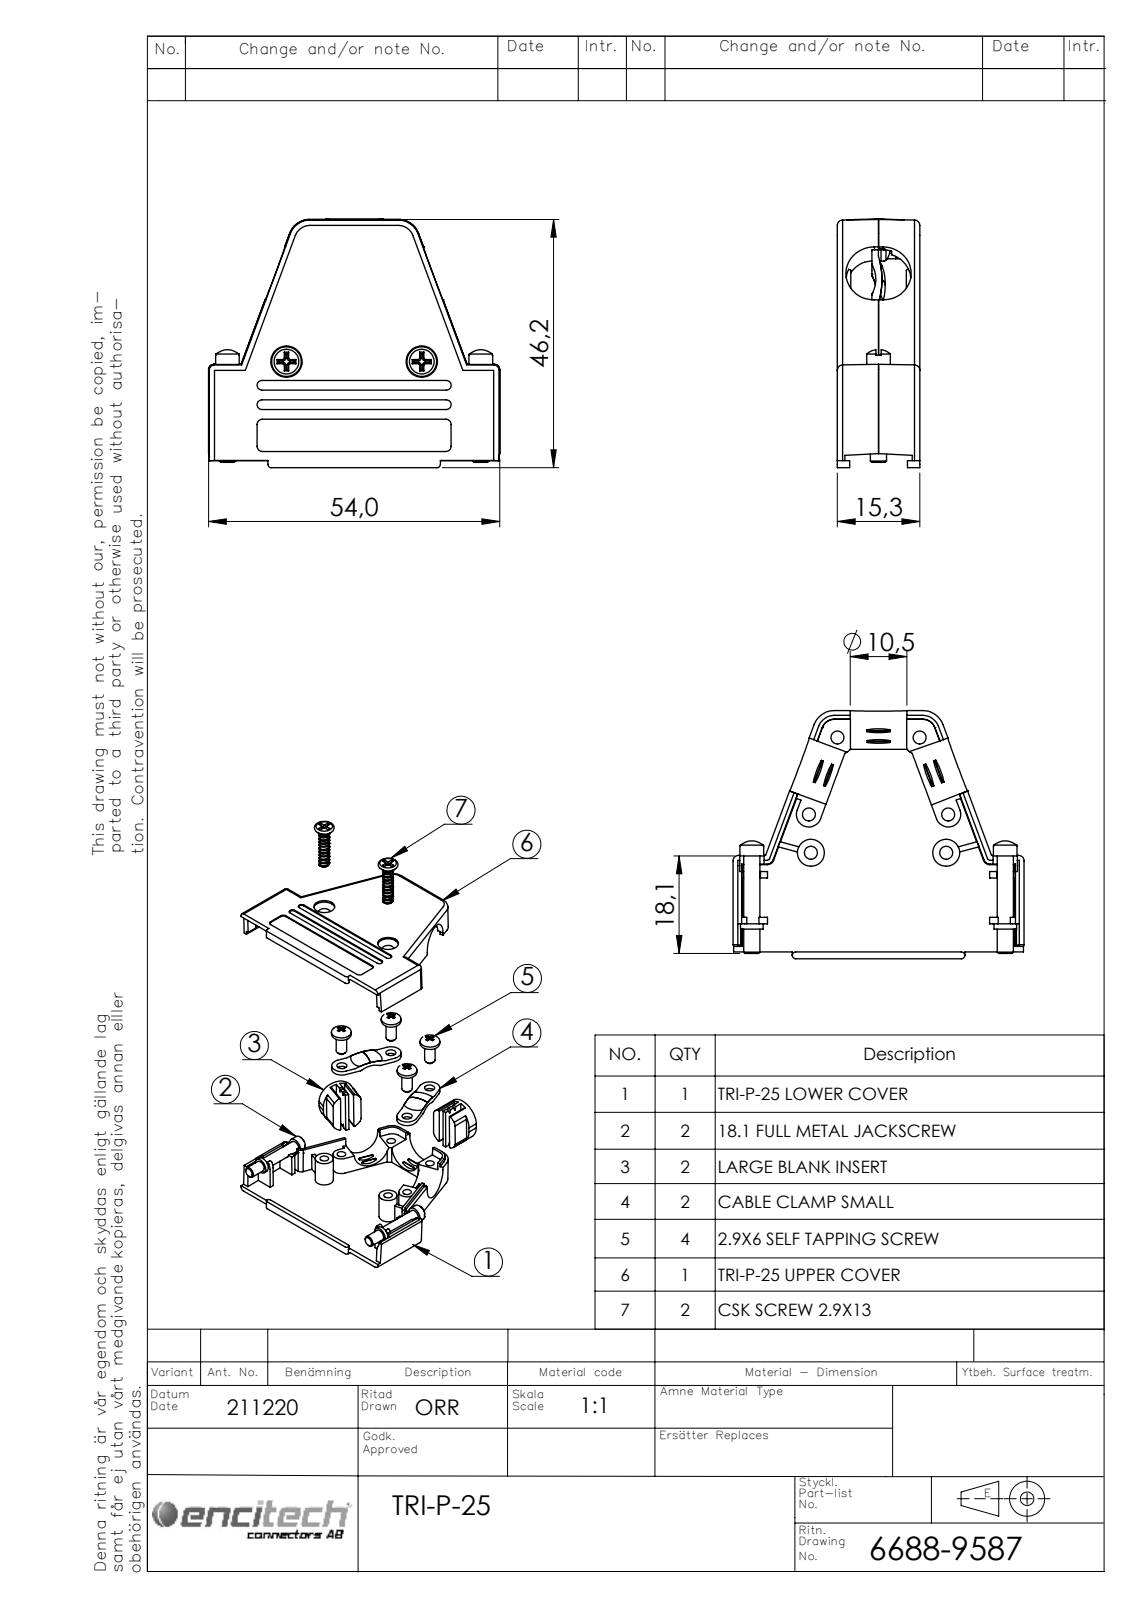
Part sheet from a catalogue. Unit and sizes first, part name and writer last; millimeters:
Units: millimetres
Overall size (bounding box): 54 × 46.19 × 15.3
Round holes (diameter × count): ⌀2.4 ×6, ⌀2.8 ×4, ⌀3.2 ×4, ⌀4.5 ×2, ⌀5.2 ×2, ⌀5.8 ×2
Round bosses / shafts (diameter × count): ⌀5.5 ×4, ⌀3 ×4, ⌀2.9 ×4, ⌀7 ×2, ⌀5 ×2, ⌀4.4 ×2, ⌀4.2 ×2, ⌀2.46 ×2
Partial cylindrical surfaces — rounded edges, fillets, slot ends (radius × count): R1 ×21, R0.5 ×10, R1.25 ×10, R0.25 ×6, R5.25 ×5, R0.9 ×4, R1.5 ×4, R1.79 ×4
Main face-to-face distances: 13.9, 1.4, 15.3, 12.5, 13.6, 1.1, 15, 6.25, 1.6, 7.65
Hole centre spacings: 15.25, 7.11, 15.14, 15.26, 21.96, 26.4, 26.44, 29.41
Volume: 9 866 mm³ · Surface area: 15 095 mm²
Bodies: 17 solids, 833 faces (454 planar, 254 cylindrical, 125 other)
Part name (STEP PRODUCT): 6805-0104-13; 6826-0133-01; 6855-0109-11; 6805-0104-03 (+4 more)
STEP written by: SolidWorks 2021 (AUTOMOTIVE_DESIGN)
